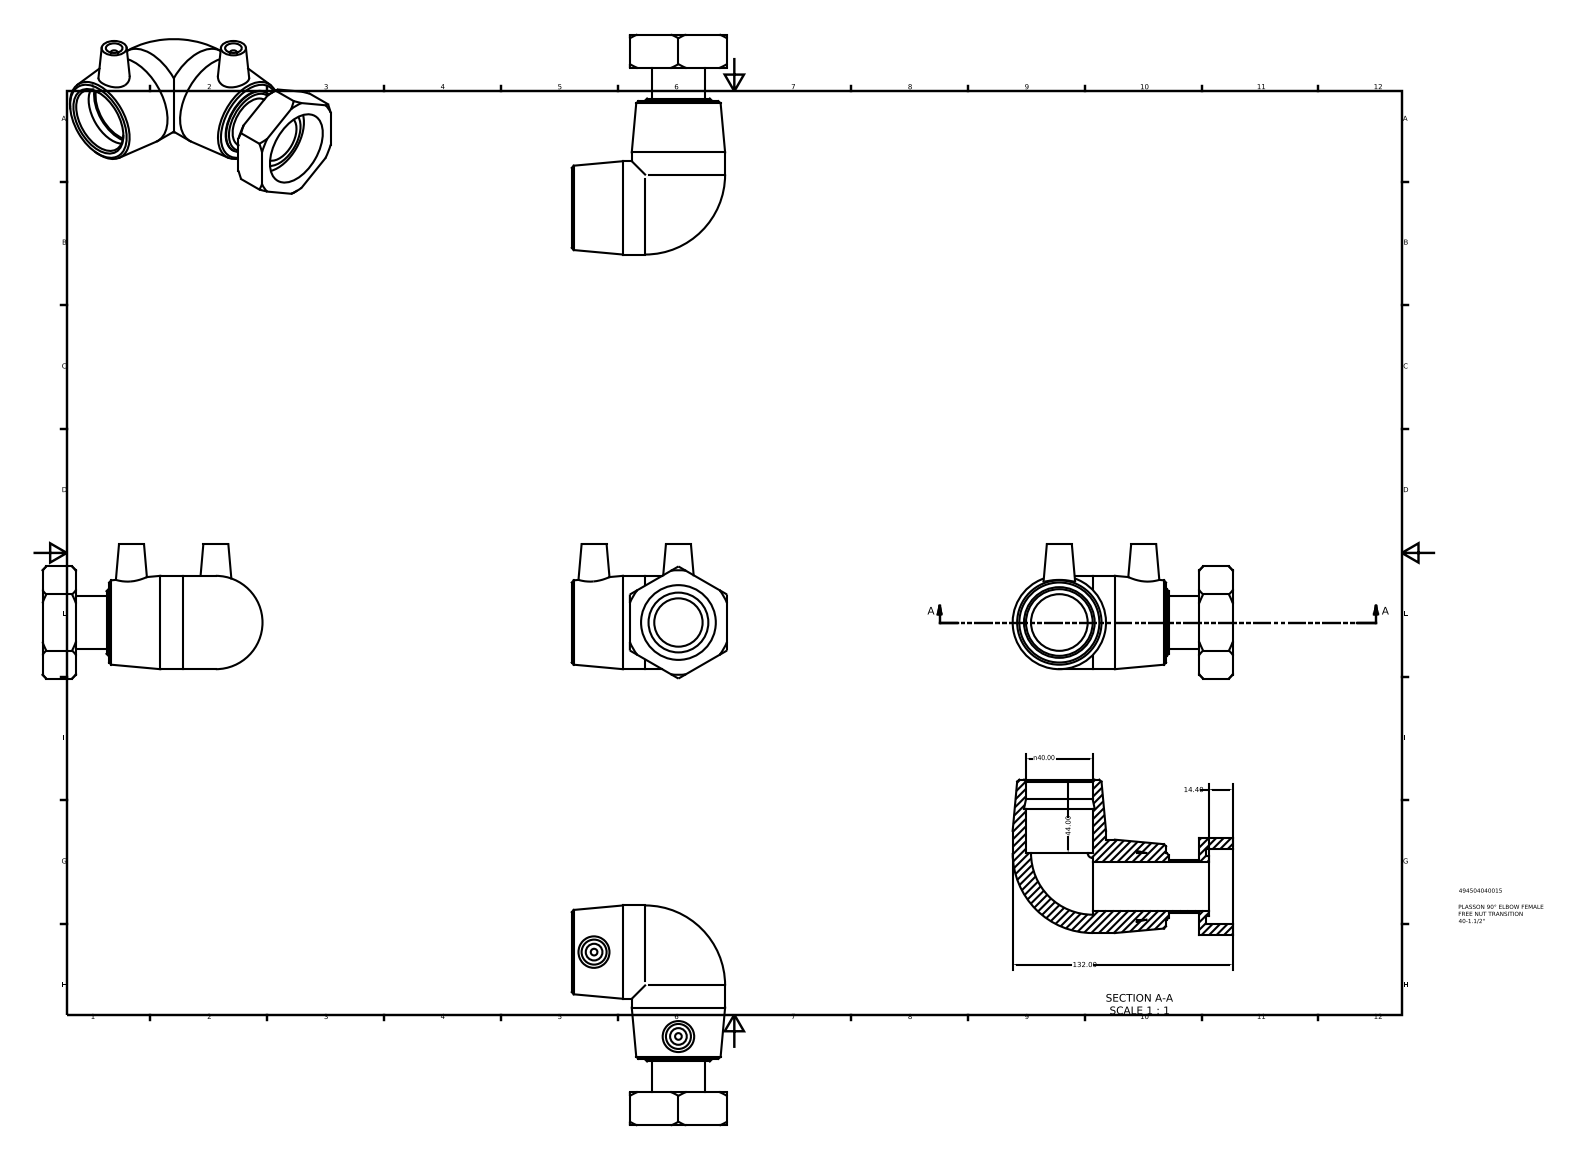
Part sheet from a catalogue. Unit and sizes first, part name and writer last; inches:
Units: inches
Overall size (bounding box): 5.197 × 3.667 × 3.174
Round holes (diameter × count): ⌀0.394 ×2, ⌀1.142 ×1, ⌀1.575 ×1, ⌀1.765 ×1
Round bosses / shafts (diameter × count): ⌀2.205 ×2, ⌀0.157 ×2, ⌀1.575 ×1, ⌀1.413 ×1, ⌀1.236 ×1
Main face-to-face distances: 2.294, 0.787, 0.945, 0.063, 1.732, 0.157, 0.63, 1.575, 1.373, 3.667
Hole centre spacings: 2.817
Volume: 12.68 in³ · Surface area: 86.45 in²
Bodies: 1 solid, 61 faces (23 planar, 14 cylindrical, 24 other)
Part name (STEP PRODUCT): 494504040015
STEP written by: Autodesk Inventor 2015 (AUTOMOTIVE_DESIGN)
